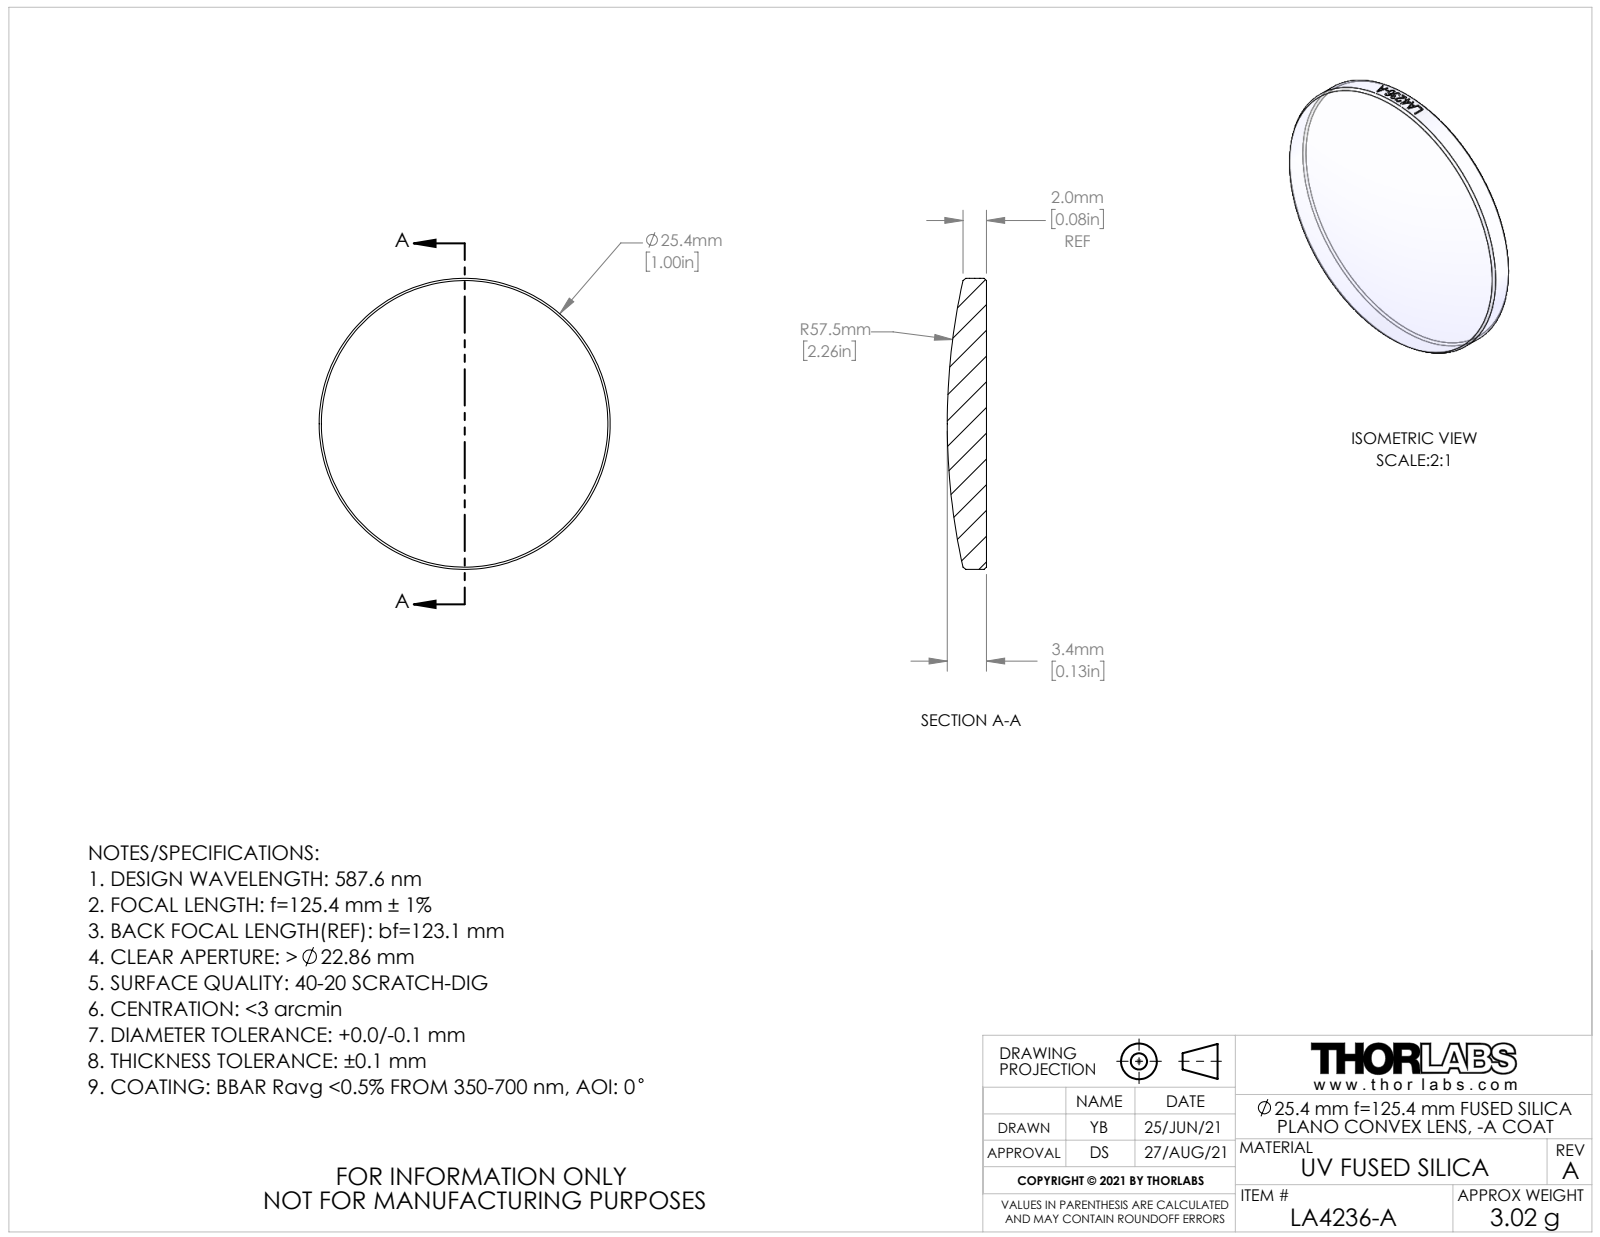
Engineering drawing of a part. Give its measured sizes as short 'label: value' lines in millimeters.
name: CTN017532-E0W; CTN017560
written by: SolidWorks 2018 (AUTOMOTIVE_DESIGN)
unit: mm
bodies: 1 solid, 21 faces (1 planar, 14 cylindrical, 6 other)
size: 25.4 × 25.4 × 3.42
volume: 1 372 mm³; area: 1 163 mm²
bosses: 1× ⌀25.4
